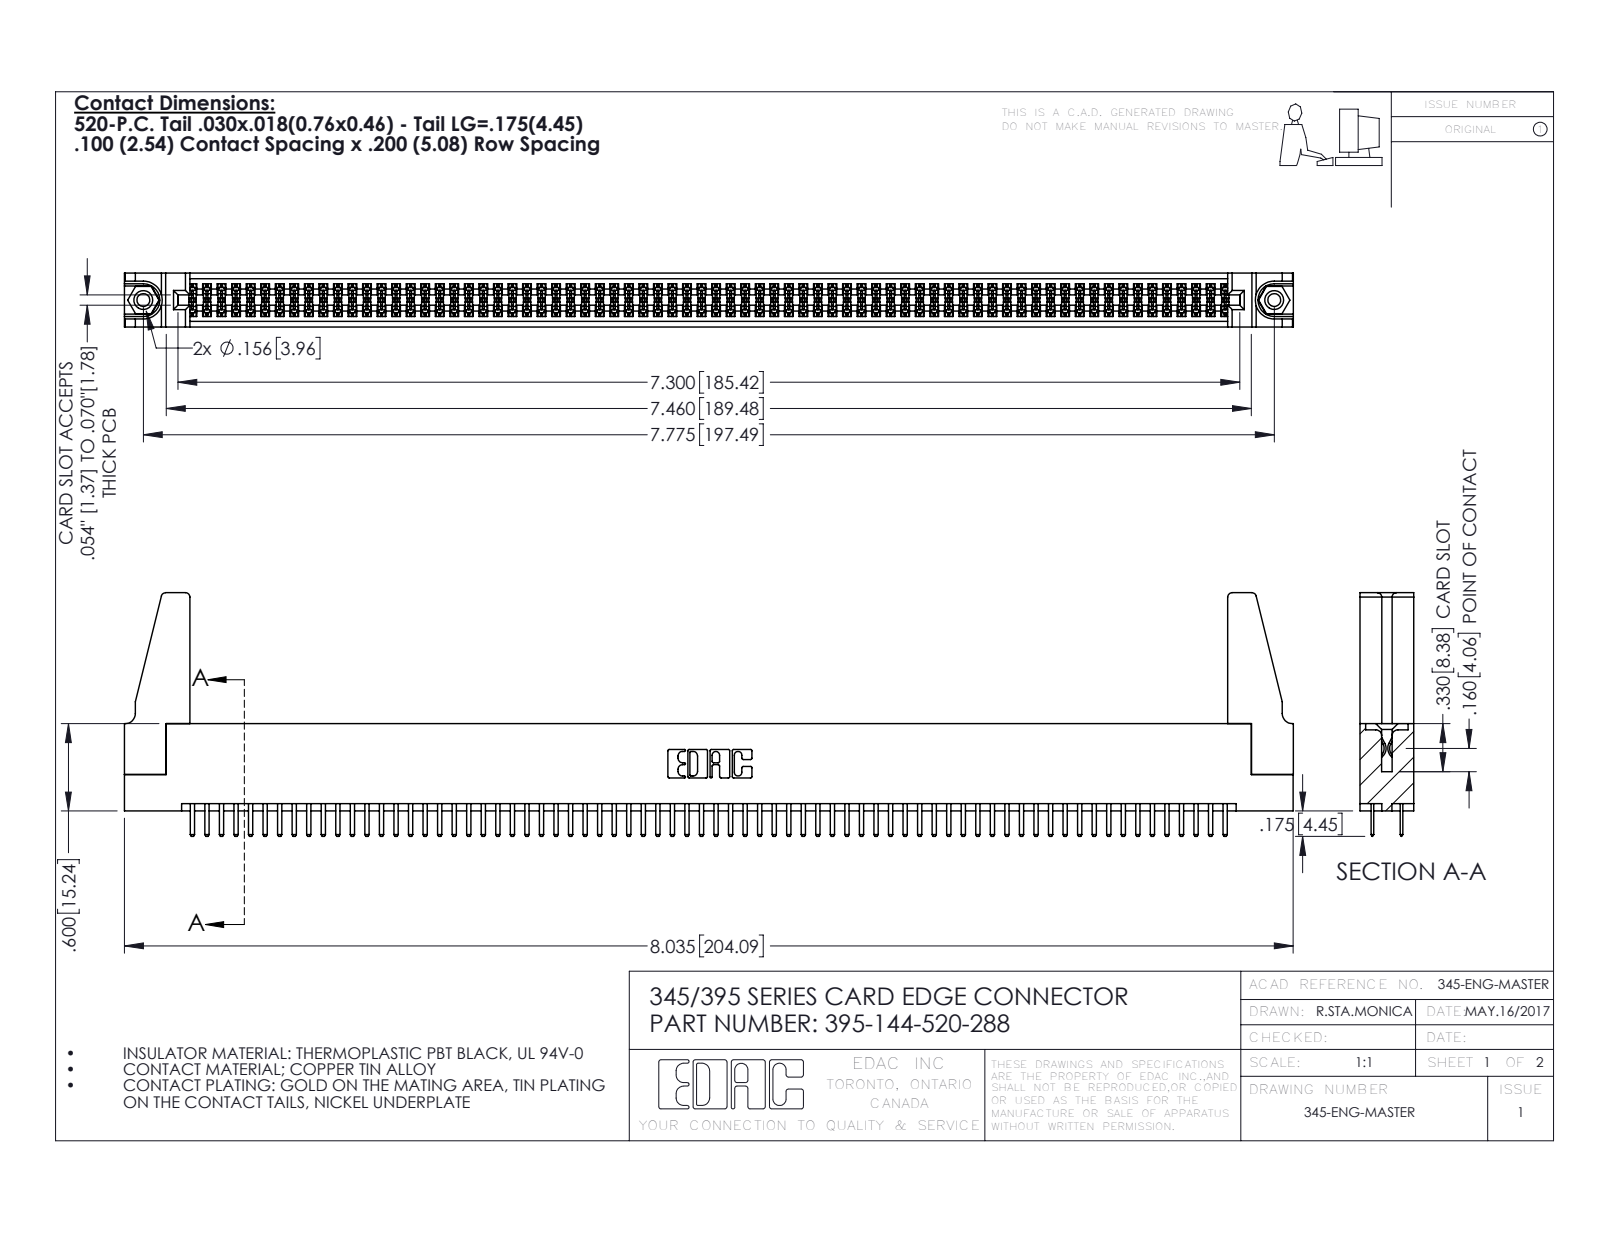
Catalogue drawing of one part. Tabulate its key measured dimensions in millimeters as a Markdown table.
| quantity | value |
| --- | --- |
| part name | 345-250-001_345-250-001-102; 345-220-078_345-220-088; 395-144-520-288; 345-292-001_345-293-120 (+1 more) |
| STEP written by | SolidWorks 2016 (CONFIG_CONTROL_DESIGN) |
| units | millimeters |
| bodies | 149 solids, 8026 faces (5192 planar, 2818 cylindrical, 16 other) |
| overall size | 204.1 × 42.5 × 9.4 |
| volume | 23 300 mm³ |
| surface area | 33 190 mm² |
| round holes (diameter × count) | 2.3 × 2, 3.2 × 2, 4 × 2, 1.6 × 1 |
| round bosses / shafts (diameter × count) | 3.9 × 2 |
| partial cylindrical surfaces (radius × count) | 0.2 × 216, 0.3 × 148, 0.3 × 22, 0.8 × 8, 0.2 × 6, 0.8 × 6, 0.7 × 3, 0.4 × 2 |
| main face-to-face distances | 1.8, 7.6, 9.4, 5.1, 2.5, 6.9, 0.6, 5.7, 0.6, 1.8 |
| hole center spacings | 6.9, 191.5, 197.5 |
